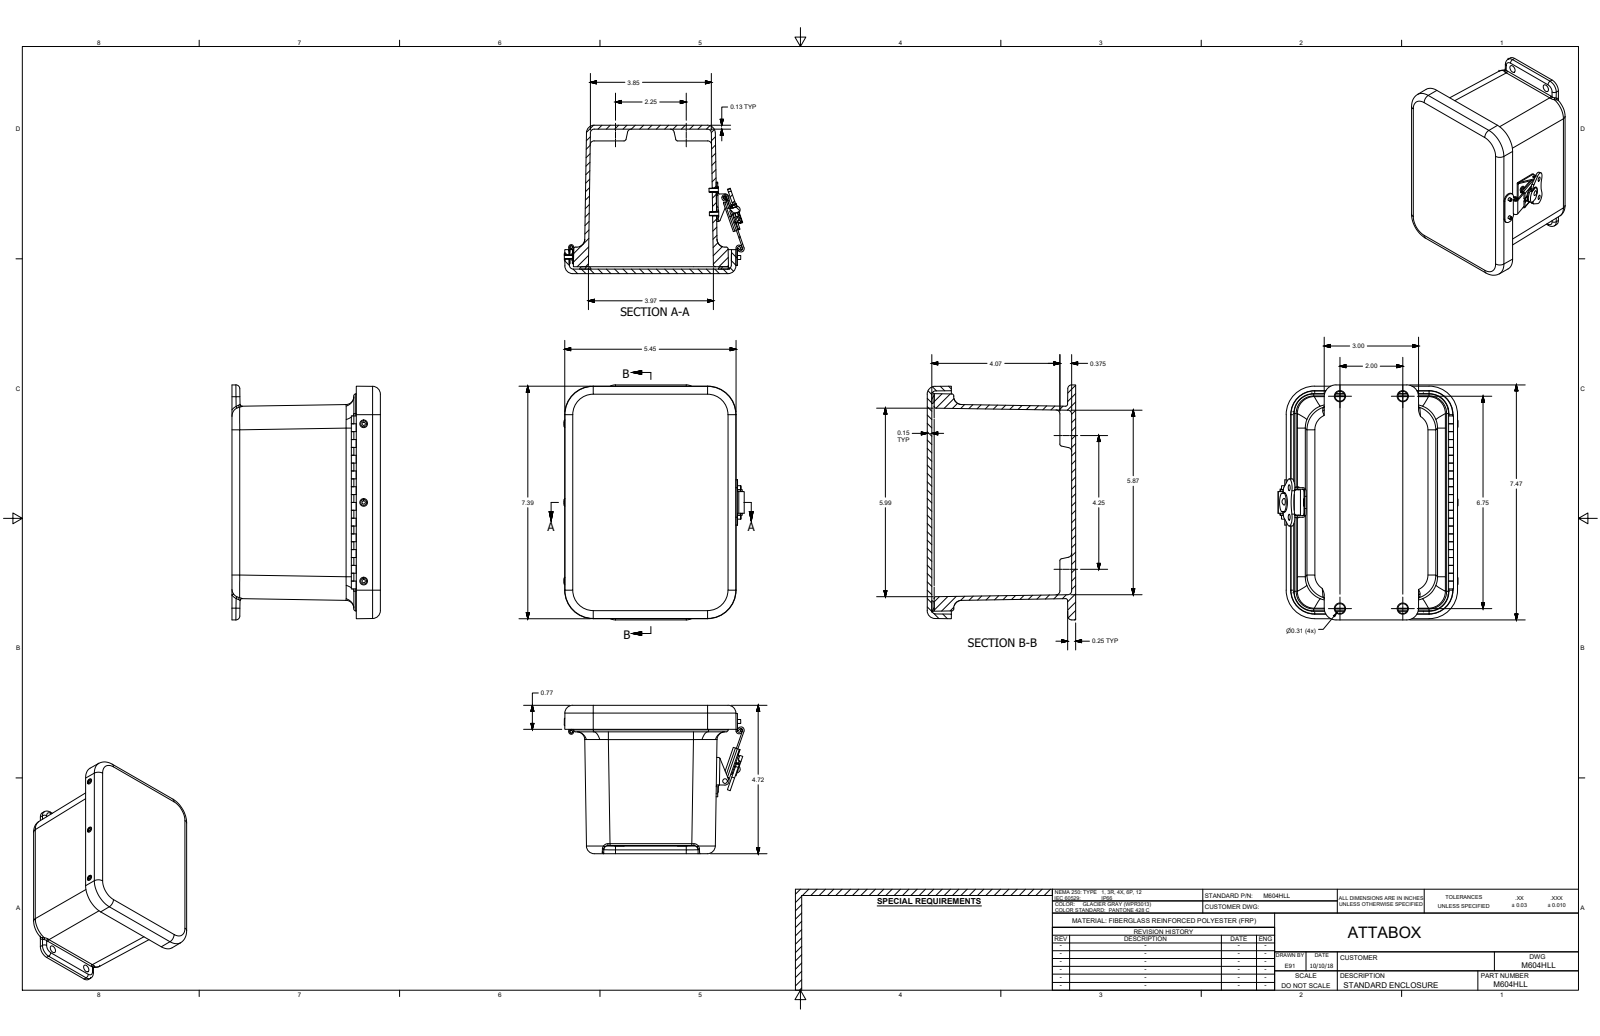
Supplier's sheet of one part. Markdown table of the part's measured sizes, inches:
| quantity | value |
| --- | --- |
| part name | M604HLL |
| STEP written by | SolidWorks 2018 (AUTOMOTIVE_DESIGN) |
| units | inches |
| bodies | 29 solids, 787 faces (290 planar, 317 cylindrical, 180 other) |
| overall size | 7.47 × 5.734 × 4.718 |
| volume | 29.4 in³ |
| surface area | 405.4 in² |
| round holes (diameter × count) | 0.14 × 10, 0.104 × 9, 0.152 × 8, 0.131 × 5, 0.159 × 4, 0.218 × 4, 0.13 × 2, 0.133 × 2, 0.187 × 2, 0.191 × 2, 0.067 × 1, 0.085 × 1 |
| round bosses / shafts (diameter × count) | 0.125 × 5, 0.125 × 5, 0.27 × 4, 0.66 × 1, 0.582 × 1, 0.525 × 1, 0.286 × 1, 0.213 × 1 |
| partial cylindrical surfaces (radius × count) | 0.125 × 43, 0.25 × 11, 0.062 × 9, 0.063 × 9, 0.015 × 8, 0.074 × 8, 0.625 × 8, 0.06 × 7 |
| main face-to-face distances | 0.145, 4.573, 4.718, 0.125, 4.448, 4.593, 4.375, 0.348, 4.5, 0.073 |
| hole center spacings | 2.5, 4, 5, 2.25, 3.339, 4.809, 6.102, 0.281 |
